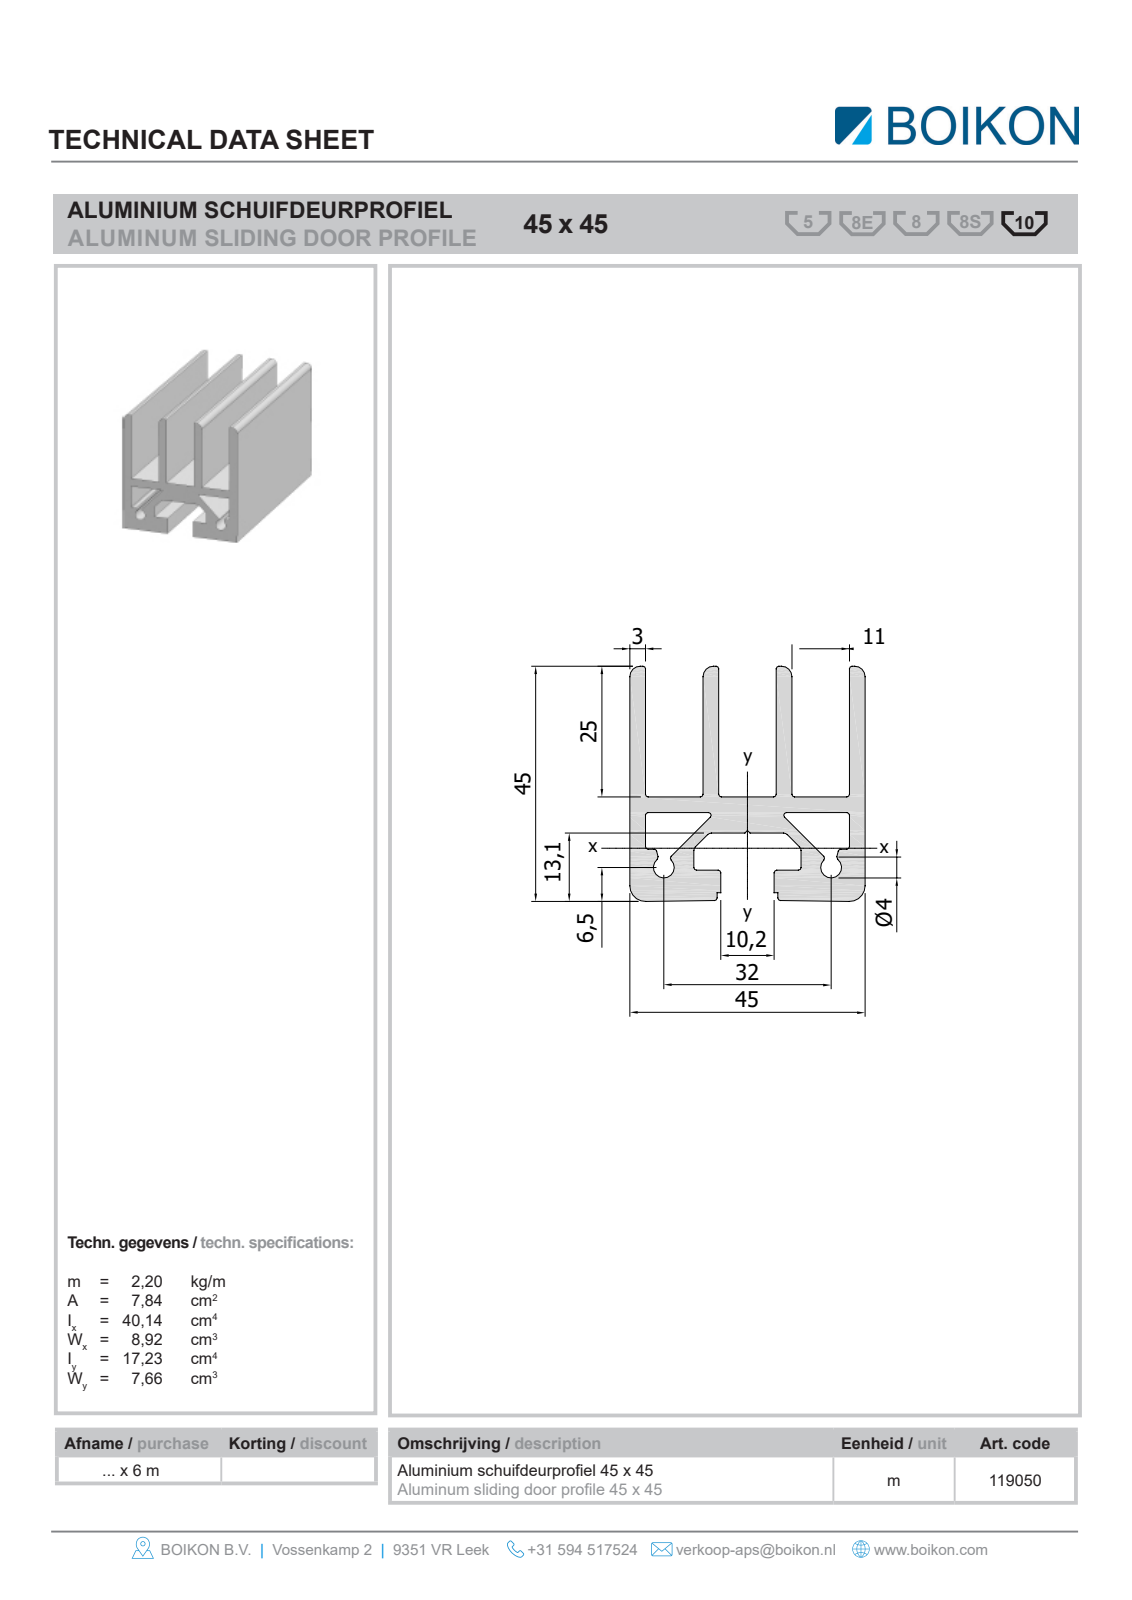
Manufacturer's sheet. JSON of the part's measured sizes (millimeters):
{"part_name": "Root; 119050Alu Schuifdeurprofiel 45x45BOIKON0", "step_written_by": "HiCAD 2013 1802.4 Build 509 (AUTOMOTIVE_DESIGN)", "units": "millimeters", "bodies": {"solids": 1, "faces": 32, "planar": 28, "cylindrical": 4, "other": 0}, "overall_size": [1000, 45, 45], "volume_mm3": 999426, "surface_area_mm2": 371733, "partial_cylinders_radius": [[2, 4]], "face_to_face_distances": [14, 3, 28, 17, 11, 25, 42, 45, 31, 20]}
